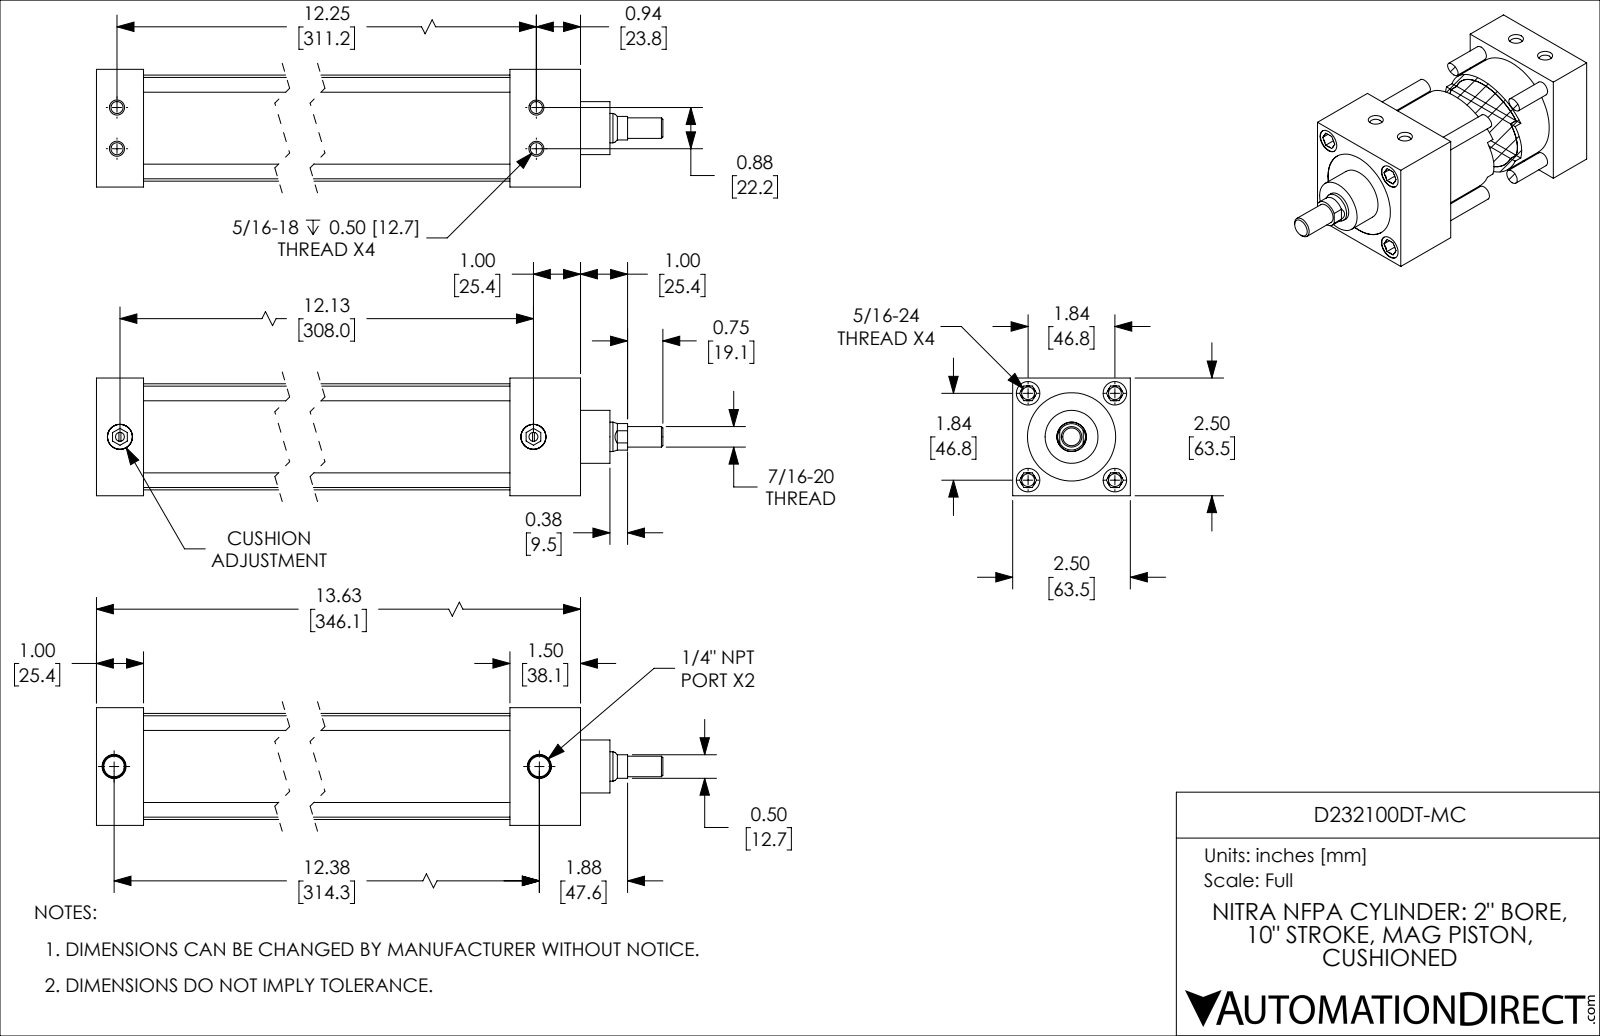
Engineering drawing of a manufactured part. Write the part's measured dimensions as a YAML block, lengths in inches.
part_name: "D232100DT-MC_BODY; D232100DT-MC_PISTON_KK1; D232100DT-MC; D232100DT-MC_CUSHION"
step_written_by: "SolidWorks 2019 (CONFIG_CONTROL_DESIGN)"
units: inches
bodies: {solids: 4, faces: 248, planar: 90, cylindrical: 78, other: 80}
overall_size: [15.375, 2.5, 2.5]
volume: 34.89
surface_area: 296.3
round_holes:
  - {diameter: 0.272, count: 7}
  - {diameter: 0.257, count: 4}
  - {diameter: 0.5, count: 4}
  - {diameter: 0.19, count: 2}
  - {diameter: 0.438, count: 2}
  - {diameter: 0.531, count: 2}
  - {diameter: 0.626, count: 1}
  - {diameter: 1.875, count: 1}
  - {diameter: 2.001, count: 1}
round_bosses_or_shafts:
  - {diameter: 0.312, count: 4}
  - {diameter: 0.532, count: 2}
  - {diameter: 2.251, count: 1}
  - {diameter: 1.999, count: 1}
  - {diameter: 1.125, count: 1}
  - {diameter: 0.624, count: 1}
  - {diameter: 0.437, count: 1}
partial_cylinders:
  - {radius: 0.281, count: 1}
face_to_face_distances: [2.5, 1, 12.125, 11.125, 1.125, 2.125, 10, 1.5, 13.625, 12.625]
hole_center_spacings: [1.84, 1.844, 1.301, 0.441, 0.443, 0.875, 1.304, 2.602]
